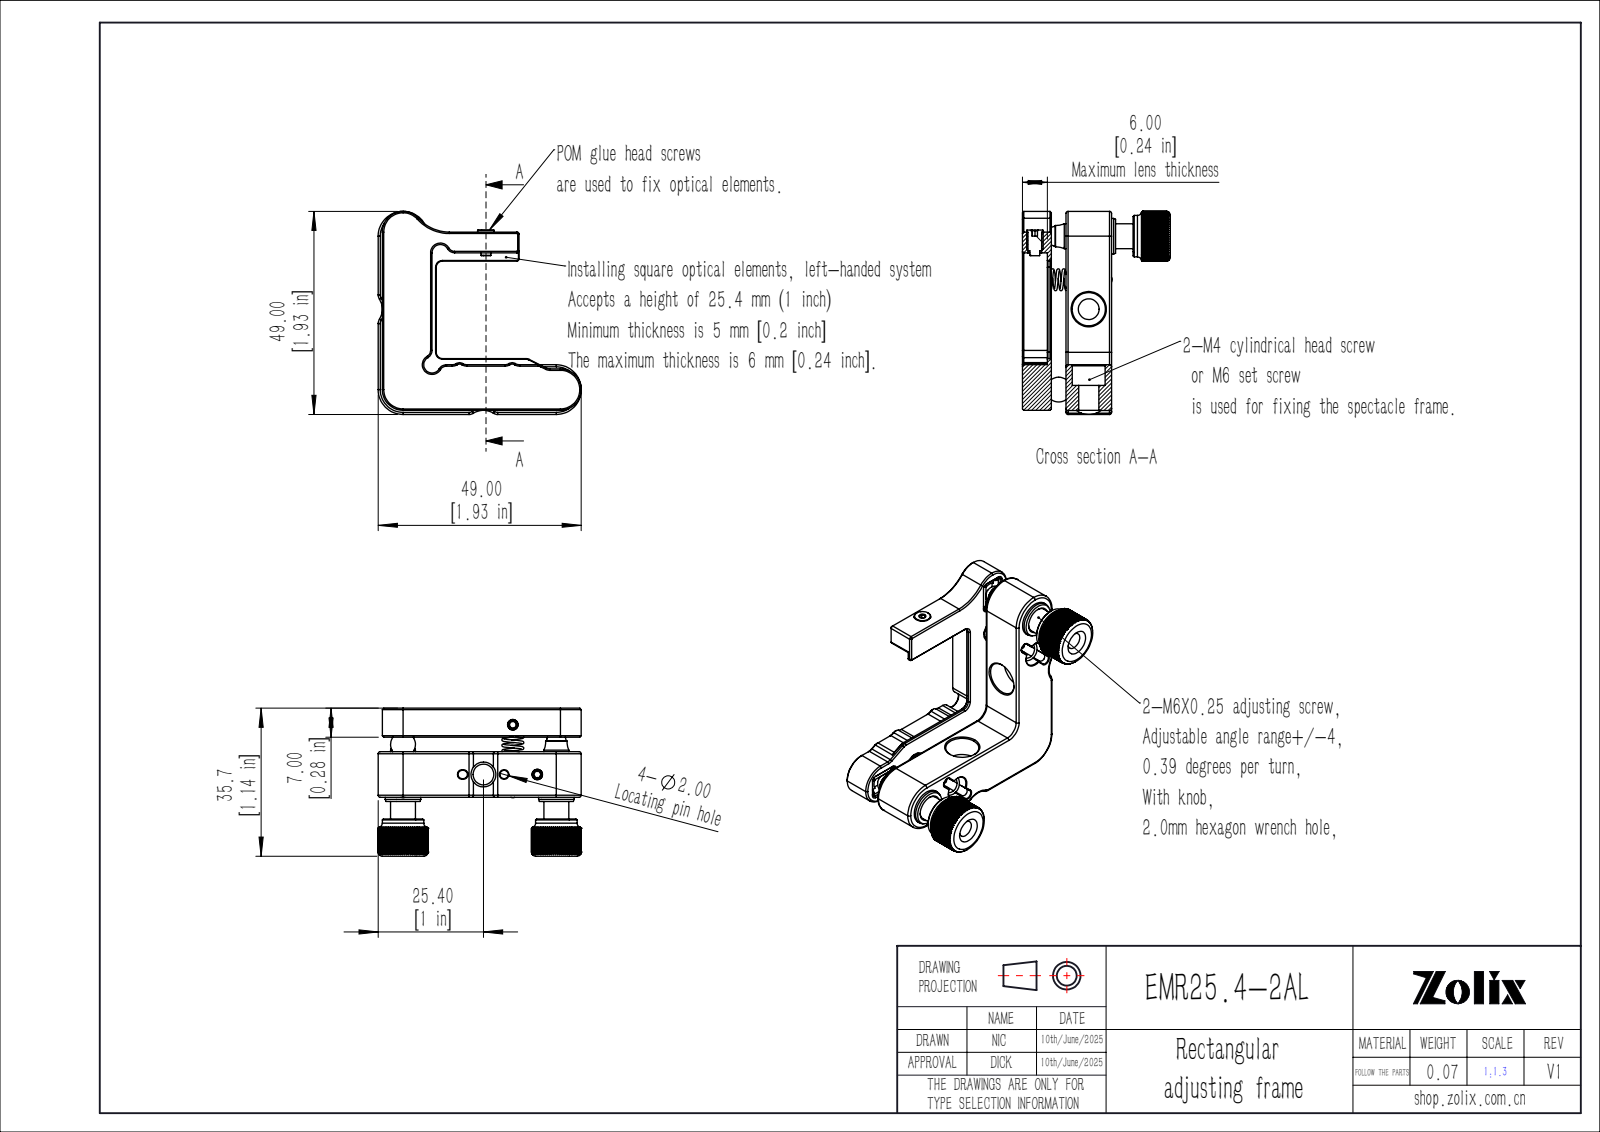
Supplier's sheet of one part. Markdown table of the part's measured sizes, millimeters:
| quantity | value |
| --- | --- |
| part name | EMR25.4-2AL |
| STEP written by | SolidWorks 2020 (CONFIG_CONTROL_DESIGN) |
| units | millimeters |
| bodies | 0 solids, 978 faces (475 planar, 293 cylindrical, 210 other) |
| overall size | 49 × 49 × 36.41 |
| round holes (diameter × count) | 6 × 4, 2.5 × 2, 4 × 2, 5 × 2, 8 × 2, 9.8 × 2, 3.3 × 1 |
| round bosses / shafts (diameter × count) | 1.5 × 4, 10 × 2, 8.6 × 2, 6 × 2, 3 × 2, 2 × 2, 4 × 1, 2.4 × 1 |
| partial cylindrical surfaces (radius × count) | 2 × 16, 0.5 × 11, 0.8 × 8, 1.1 × 4, 1.25 × 4, 1.5 × 4, 5 × 3, 6 × 3 |
| main face-to-face distances | 11, 1, 7.7, 3.5, 11.2, 12, 22.2, 14.5, 8.2, 13 |
| hole center spacings | 5, 10.5, 45.51, 13.36, 14.06, 37.48, 52.33 |
